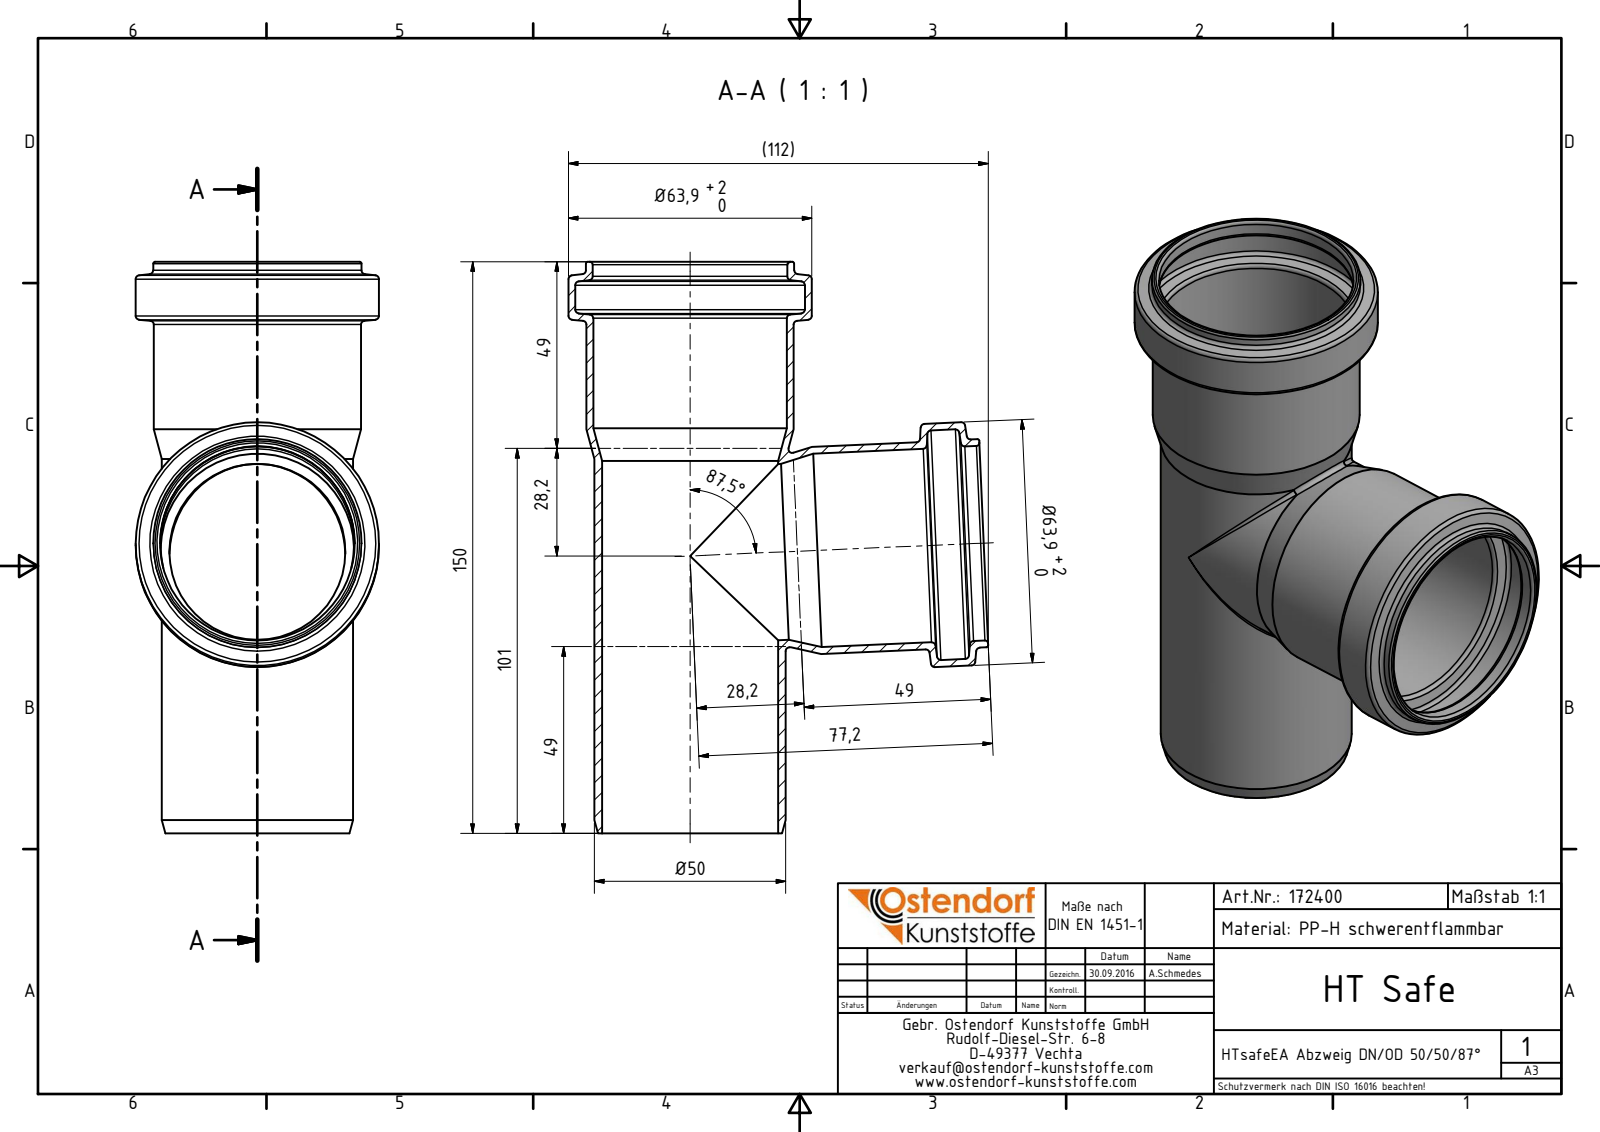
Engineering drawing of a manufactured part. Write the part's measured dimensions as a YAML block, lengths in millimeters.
part_name: "172400 HTsafeEA DN_OD 50_50_87°"
step_written_by: "Autodesk Inventor 2016 (AUTOMOTIVE_DESIGN)"
units: millimeters
bodies: {solids: 1, faces: 56, planar: 3, cylindrical: 16, other: 37}
overall_size: [150, 110.25, 63.9]
volume: 65194
surface_area: 69216
round_holes:
  - {diameter: 46.2, count: 2}
  - {diameter: 50.8, count: 2}
  - {diameter: 51.1, count: 2}
  - {diameter: 60.3, count: 2}
round_bosses_or_shafts:
  - {diameter: 63.9, count: 2}
  - {diameter: 54.7, count: 2}
  - {diameter: 54.4, count: 2}
  - {diameter: 50.2, count: 2}
face_to_face_distances: [150]
